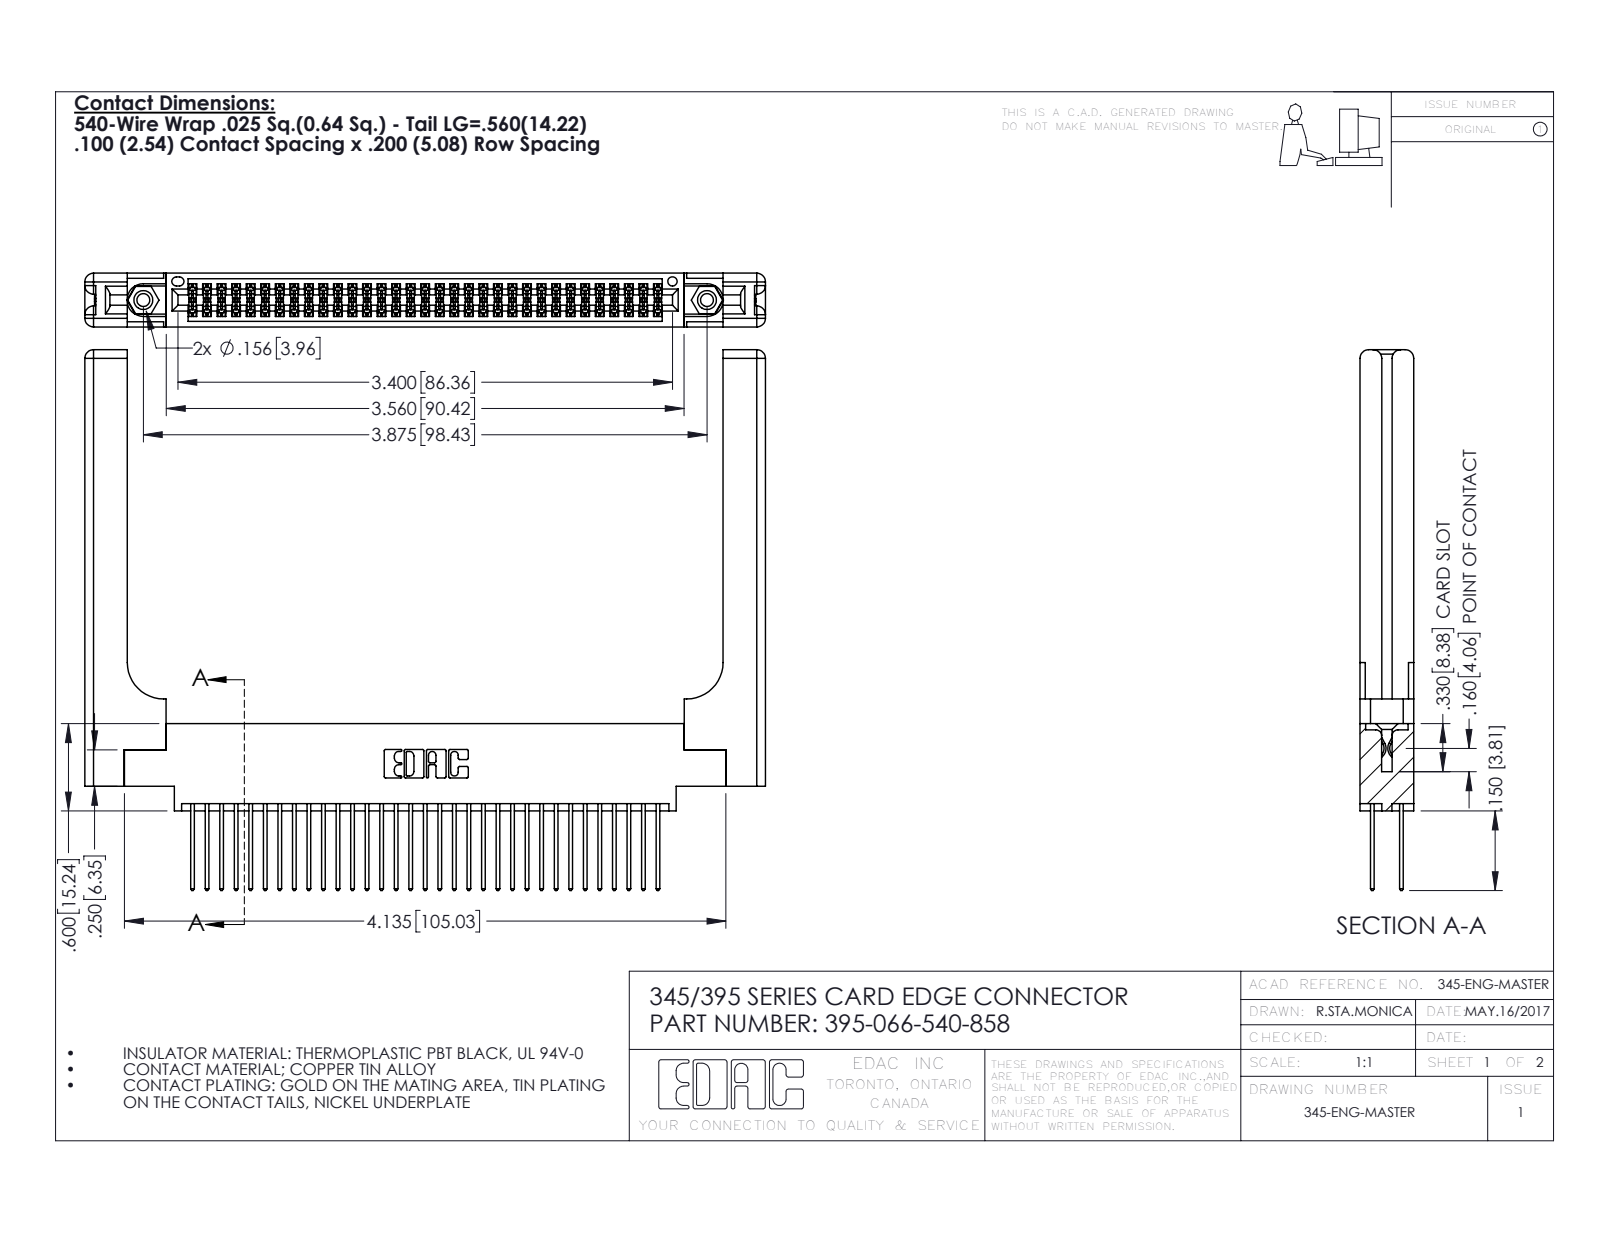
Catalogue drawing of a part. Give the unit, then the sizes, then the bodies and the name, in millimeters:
Units: millimetres
Overall size (bounding box): 118.8 × 94.4 × 9.4
Round holes (diameter × count): ⌀2.3 ×2, ⌀3.2 ×2, ⌀4 ×2, ⌀1.6 ×1
Round bosses / shafts (diameter × count): ⌀3.9 ×2
Partial cylindrical surfaces — rounded edges, fillets, slot ends (radius × count): R0.2 ×99, R0.3 ×66, R0.3 ×22, R1.5 ×16, R0.2 ×6, R0.8 ×6, R0.7 ×3, R0.4 ×2
Main face-to-face distances: 1.8, 7.6, 9.4, 2.5, 6.9, 0.6, 5.1, 5.7, 4.4, 3.8
Hole centre spacings: 6.9, 92.5, 98.4
Volume: 20 070 mm³ · Surface area: 23 340 mm²
Bodies: 71 solids, 3686 faces (2410 planar, 1216 cylindrical, 60 other)
Part name (STEP PRODUCT): 345 Part_0.170 Offset - 0.156 Dia-TH; 345-220-058_345-220-058; 345-250-001_345-250-001-102; 345-292-001_345-293-140 (+1 more)
STEP written by: SolidWorks 2016 (CONFIG_CONTROL_DESIGN)
